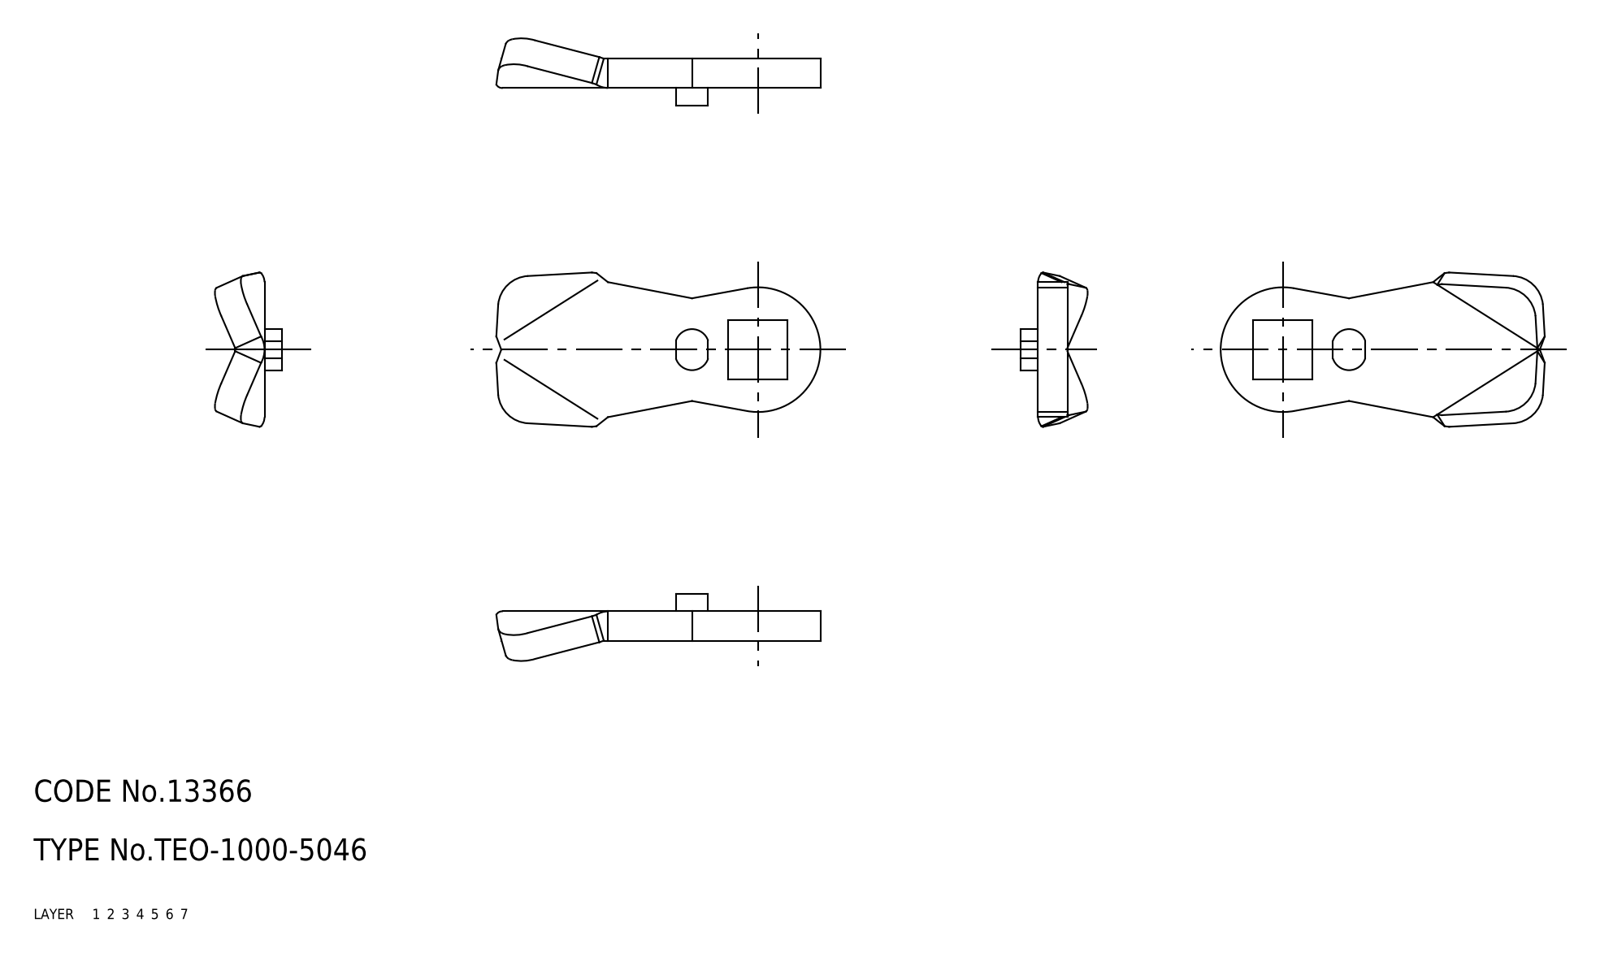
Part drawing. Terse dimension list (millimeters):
name: cam
written by: CADfix (AUTOMOTIVE_DESIGN)
unit: mm
bodies: 1 solid, 47 faces (0 planar, 0 cylindrical, 47 other)
size: 44.17 × 21.07 × 10.03
volume: 2 775 mm³; area: 2 080 mm²
